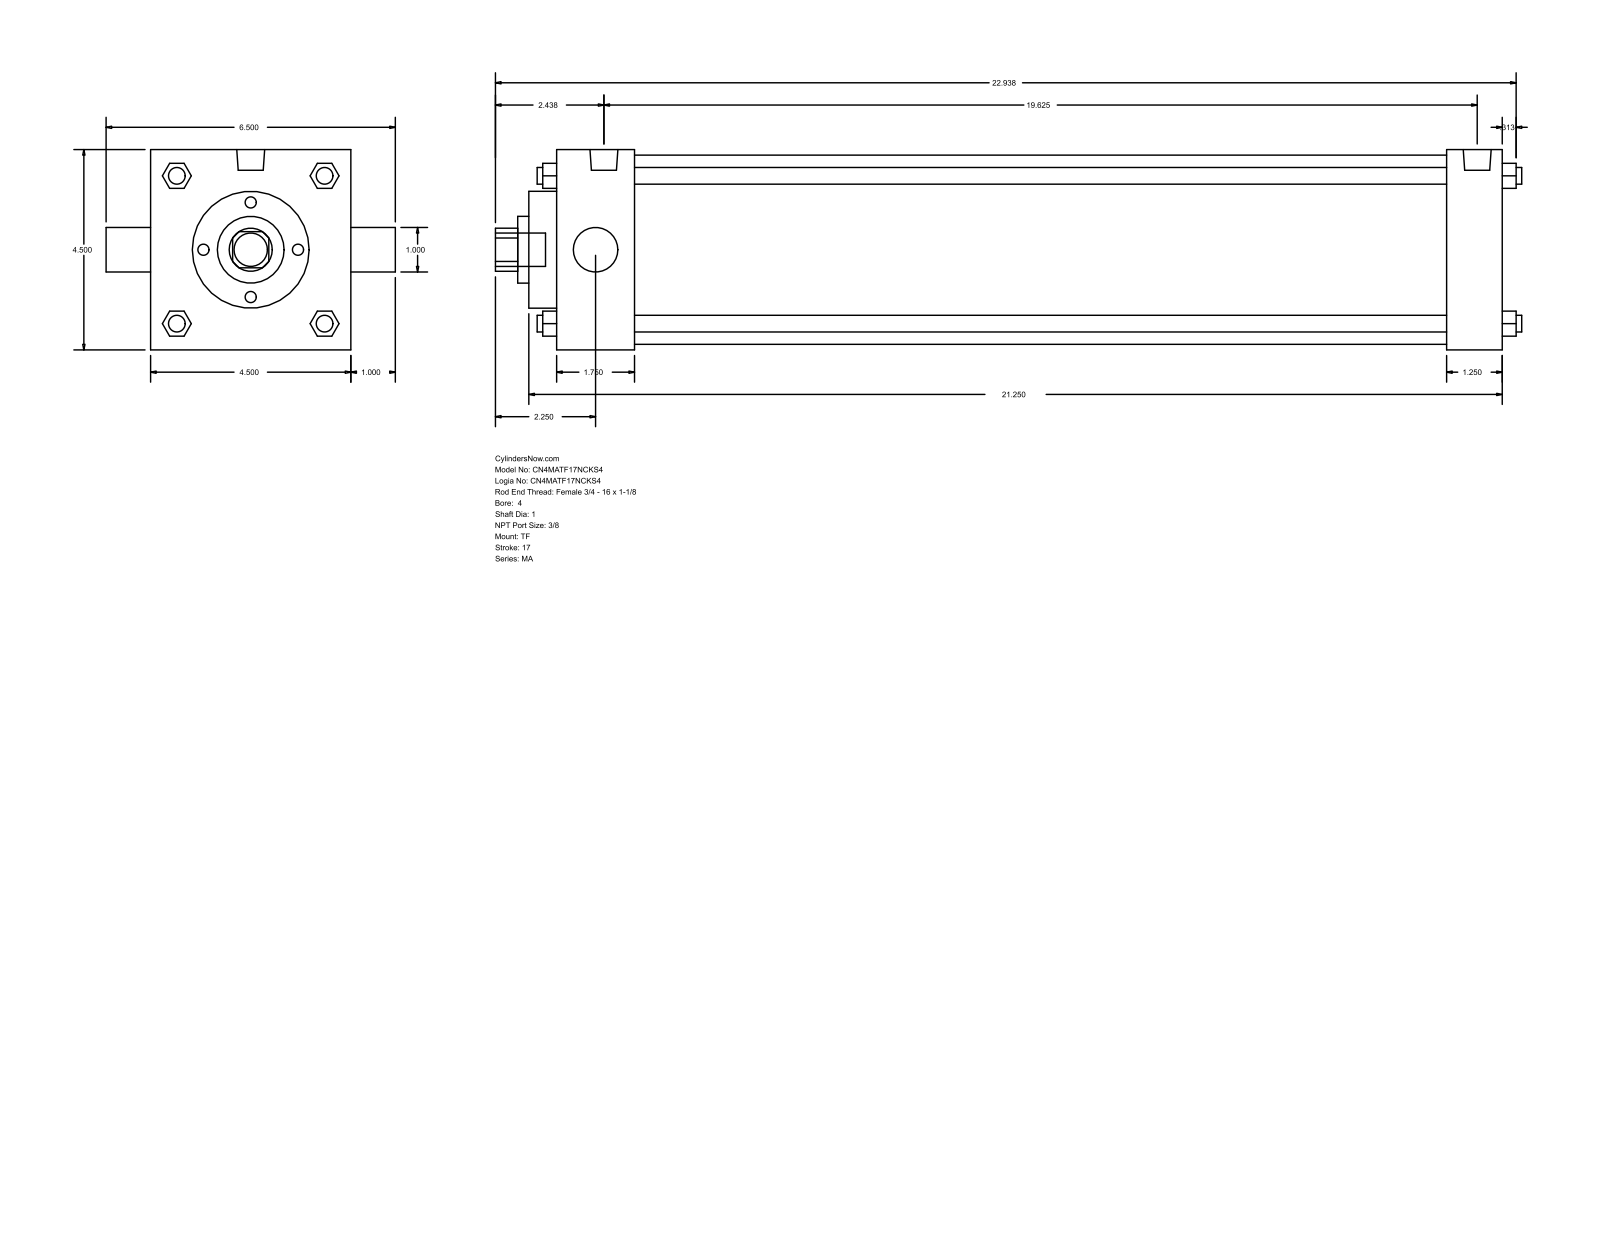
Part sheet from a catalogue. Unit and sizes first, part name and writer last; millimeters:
Units: millimetres
Overall size (bounding box): 585.79 × 165.1 × 114.3
Round holes (diameter × count): ⌀25.4 ×2, ⌀38.1 ×1, ⌀66.67 ×1, ⌀107.95 ×1
Round bosses / shafts (diameter × count): ⌀9.53 ×4, ⌀11.11 ×3, ⌀15.93 ×2, ⌀19.05 ×1
Partial cylindrical surfaces — rounded edges, fillets, slot ends (radius × count): R12.29 ×1
Main face-to-face distances: 114.3, 539.75, 508, 31.75, 44.46, 463.54, 495.29, 555.62, 15.87, 60.33
Bodies: 0 solids, 122 faces (93 planar, 29 cylindrical, 0 other)
Part name (STEP PRODUCT): MA_TF__0400_1
STEP written by: GSSL Pune (CONFIG_CONTROL_DESIGN)
